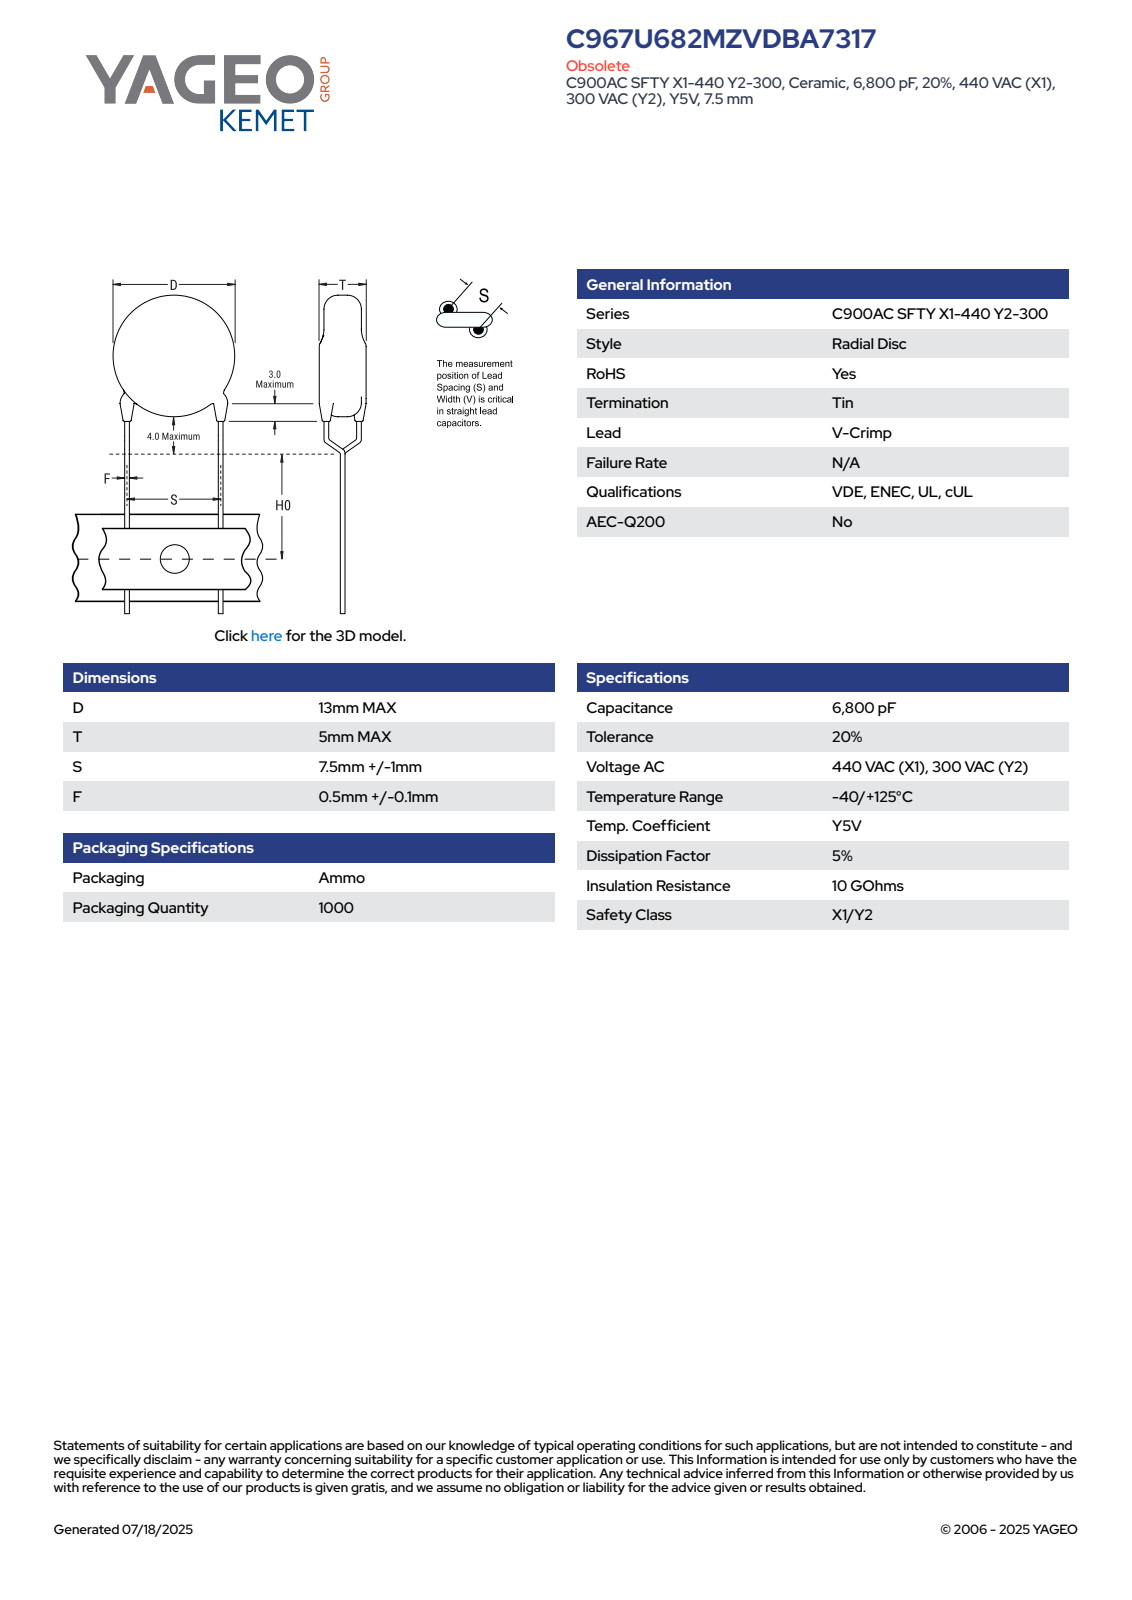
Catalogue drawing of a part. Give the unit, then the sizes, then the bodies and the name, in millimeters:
Units: millimetres
Overall size (bounding box): 36.8 × 13 × 5
Round bosses / shafts (diameter × count): ⌀0.6 ×6, ⌀13 ×1
Main face-to-face distances: 5, 22.9, 31.14, 8.24, 29.45, 6.55, 1.69, 0.46, 6.9, 0.63
Volume: 662 mm³ · Surface area: 549 mm²
Bodies: 5 solids, 93 faces (65 planar, 16 cylindrical, 12 other)
Part name (STEP PRODUCT): CCD_VCC900_D13T5S7.5LL20F0.6
STEP written by: SolidWorks 2014 (AUTOMOTIVE_DESIGN)
